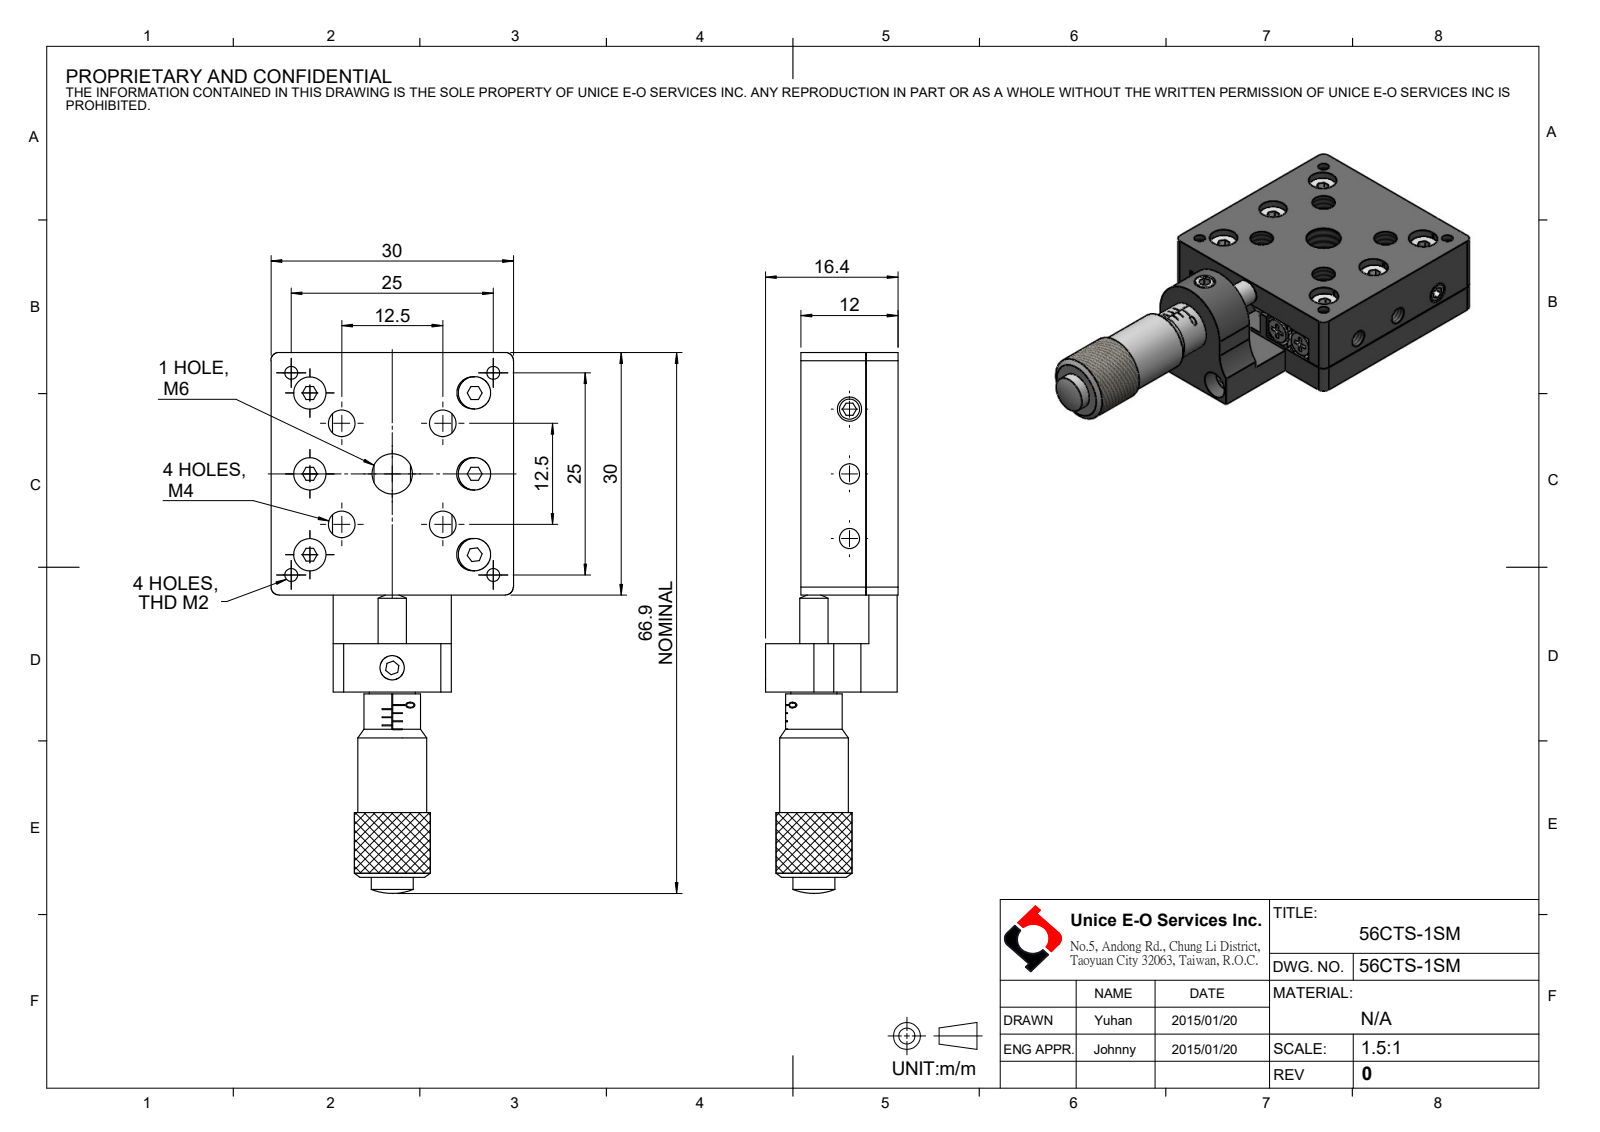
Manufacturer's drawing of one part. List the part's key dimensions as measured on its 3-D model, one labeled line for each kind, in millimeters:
Part name (STEP PRODUCT): 56CTS-1SM
STEP written by: SolidWorks 2016 (CONFIG_CONTROL_DESIGN)
Units: millimetres
Bodies: 36 solids, 941 faces (540 planar, 278 cylindrical, 123 other)
Overall size (bounding box): 66.9 × 30 × 16.4
Volume: 12 153 mm³ · Surface area: 13 550 mm²
Round holes (diameter × count): ⌀1.6 ×24, ⌀4 ×11, ⌀2.5 ×7, ⌀2.4 ×6, ⌀3.3 ×4, ⌀2.1 ×2, ⌀3 ×1, ⌀3.5 ×1, ⌀5 ×1, ⌀6 ×1
Round bosses / shafts (diameter × count): ⌀2 ×16, ⌀4 ×5, ⌀3.6 ×4, ⌀1.95 ×4, ⌀3.8 ×2, ⌀3 ×2, ⌀9.4 ×1, ⌀8.5 ×1
Partial cylindrical surfaces — rounded edges, fillets, slot ends (radius × count): R1.25 ×6, R1 ×4, R2 ×3, R5 ×2, R6 ×1
Main face-to-face distances: 3.9, 4, 8.1, 4.1, 7.9, 12, 3, 3.8, 15.5, 30
Hole centre spacings: 10, 8.84, 11.14, 15.5, 18.45, 19.76, 4.9, 17.68
